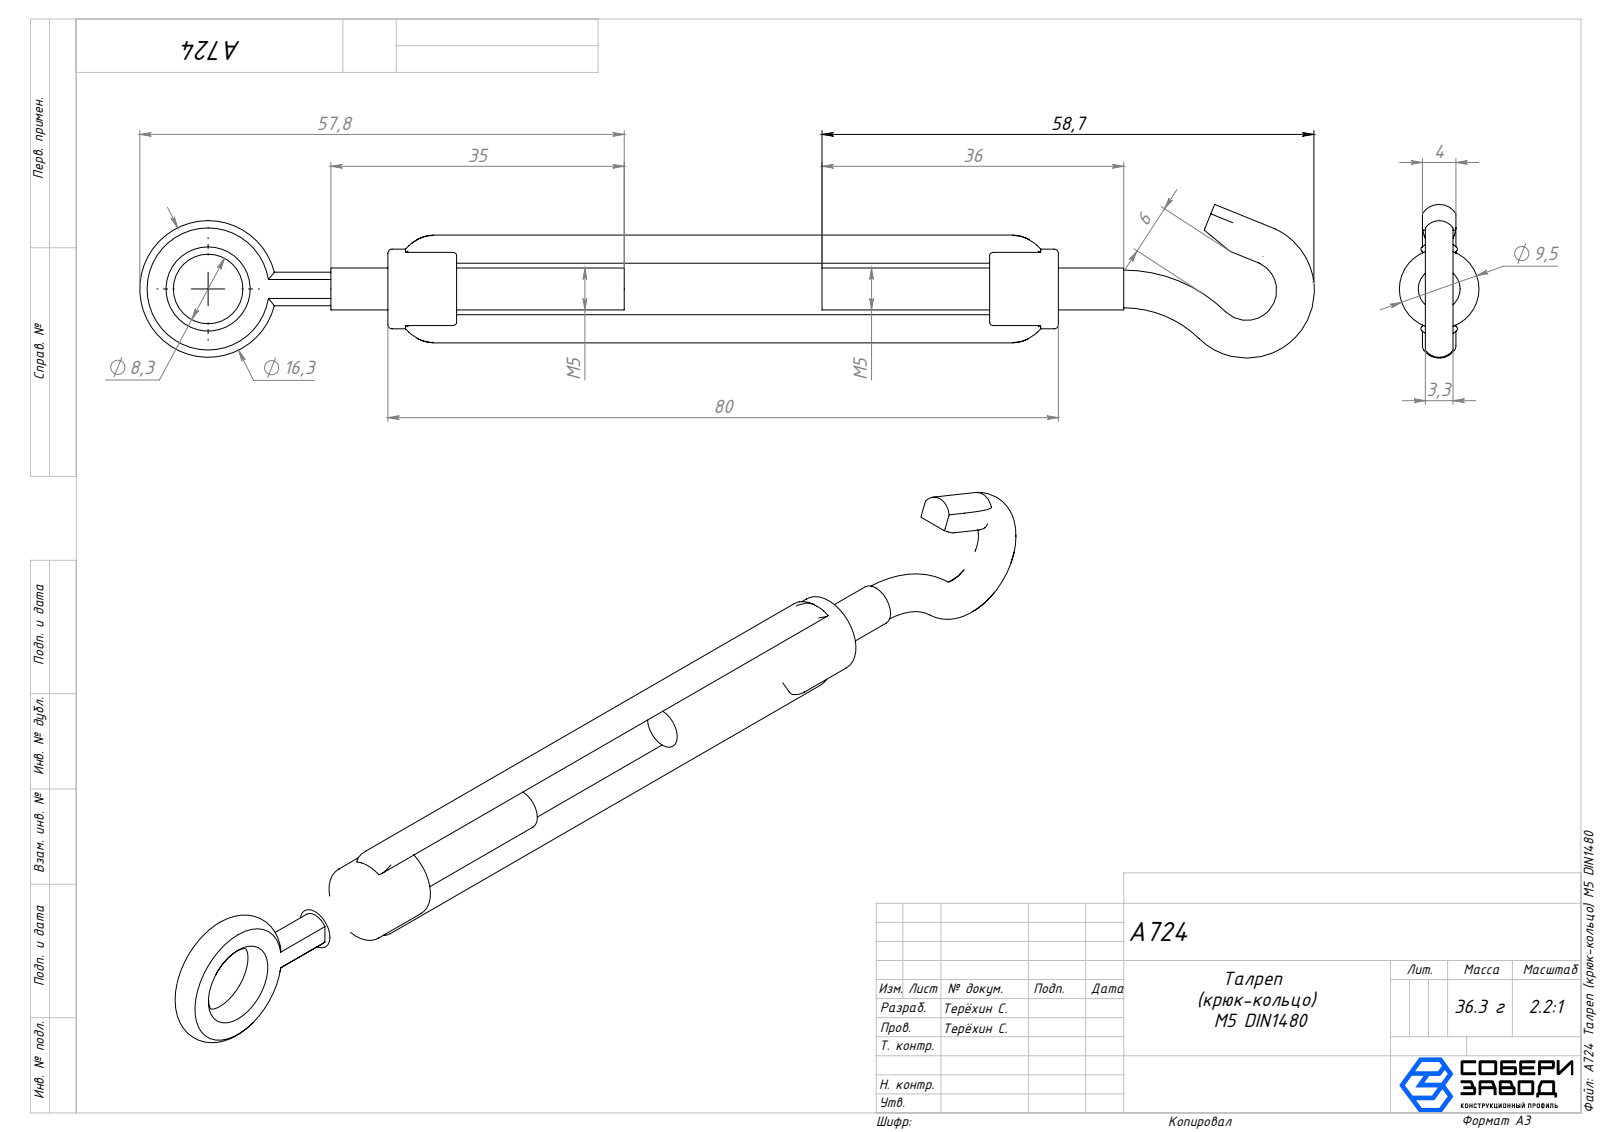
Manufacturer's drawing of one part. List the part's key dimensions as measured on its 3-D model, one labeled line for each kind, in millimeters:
Part name (STEP PRODUCT): Талреп основание_00; Талреп крюк_00; Сборка2; A724 Талреп (крюк-кольцо) М5 DIN1480_00 (+1 more)
STEP written by: SolidWorks 2025 (AUTOMOTIVE_DESIGN)
Units: millimetres
Bodies: 3 solids, 97 faces (22 planar, 29 cylindrical, 46 other)
Overall size (bounding box): 140.15 × 18.34 × 9.5
Volume: 4 621 mm³ · Surface area: 4 668 mm²
Round holes (diameter × count): ⌀4 ×1
Round bosses / shafts (diameter × count): ⌀9.5 ×1, ⌀5 ×1
Partial cylindrical surfaces — rounded edges, fillets, slot ends (radius × count): R0.3 ×8, R1 ×2, R2.25 ×1
Main face-to-face distances: 10.5, 2.82, 7.67, 4.85, 7.68, 2.83, 3.3, 8.2, 71.8, 3.65
